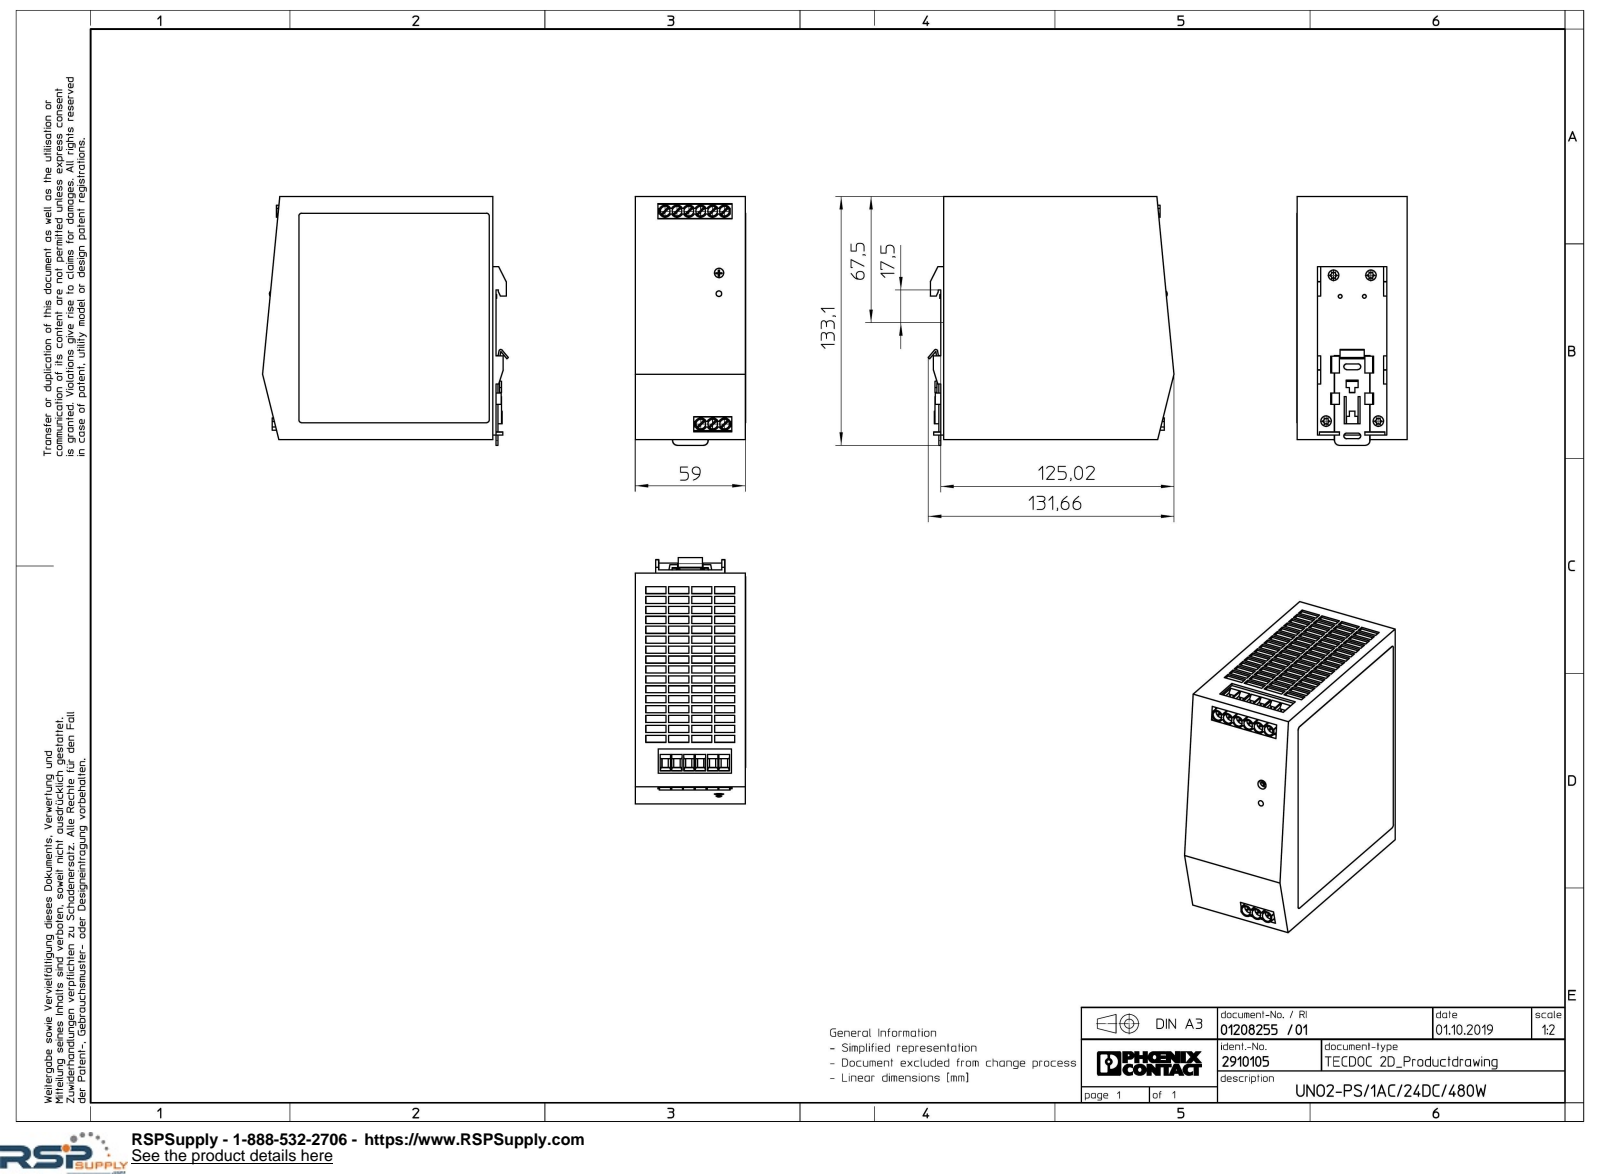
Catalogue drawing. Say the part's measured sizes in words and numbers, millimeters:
The part is named "UNO2_PS_1AC_24DC_480W-select". Its 3-D file was written by "Creo Elements/Direct Modeling 20.1A 29-Sep-2018 (C) Parametric Technology GmbH (AUTOMOTIVE_DESIGN)". It is 1 solid with 1149 faces: 1086 planar, 61 cylindrical and 2 other. Overall it measures 133.1 by 131.66 by 59.1 millimeters. Its volume is 911 253 cubic millimeters and its surface area 69 807 square millimeters. Round holes: 9 of diameter 5.2, 4 of diameter 5.6, 1 of diameter 5. Round bosses or shafts: 2 of diameter 2. Partial cylindrical surfaces (rounded edges, fillets, slot ends): 9 of radius 3.25, 8 of radius 1.5, 2 of radius 2.5, 1 of radius 1. The main face-to-face distances are 59.1, 1, 129.03, 59, 130.03, 1.6, 128.03, 2.6, 12.3, 48. The hole center spacings are 6.35, 113.8, 113.98, 114.51, 6.36, 12.7, 12.71, 19.05.
